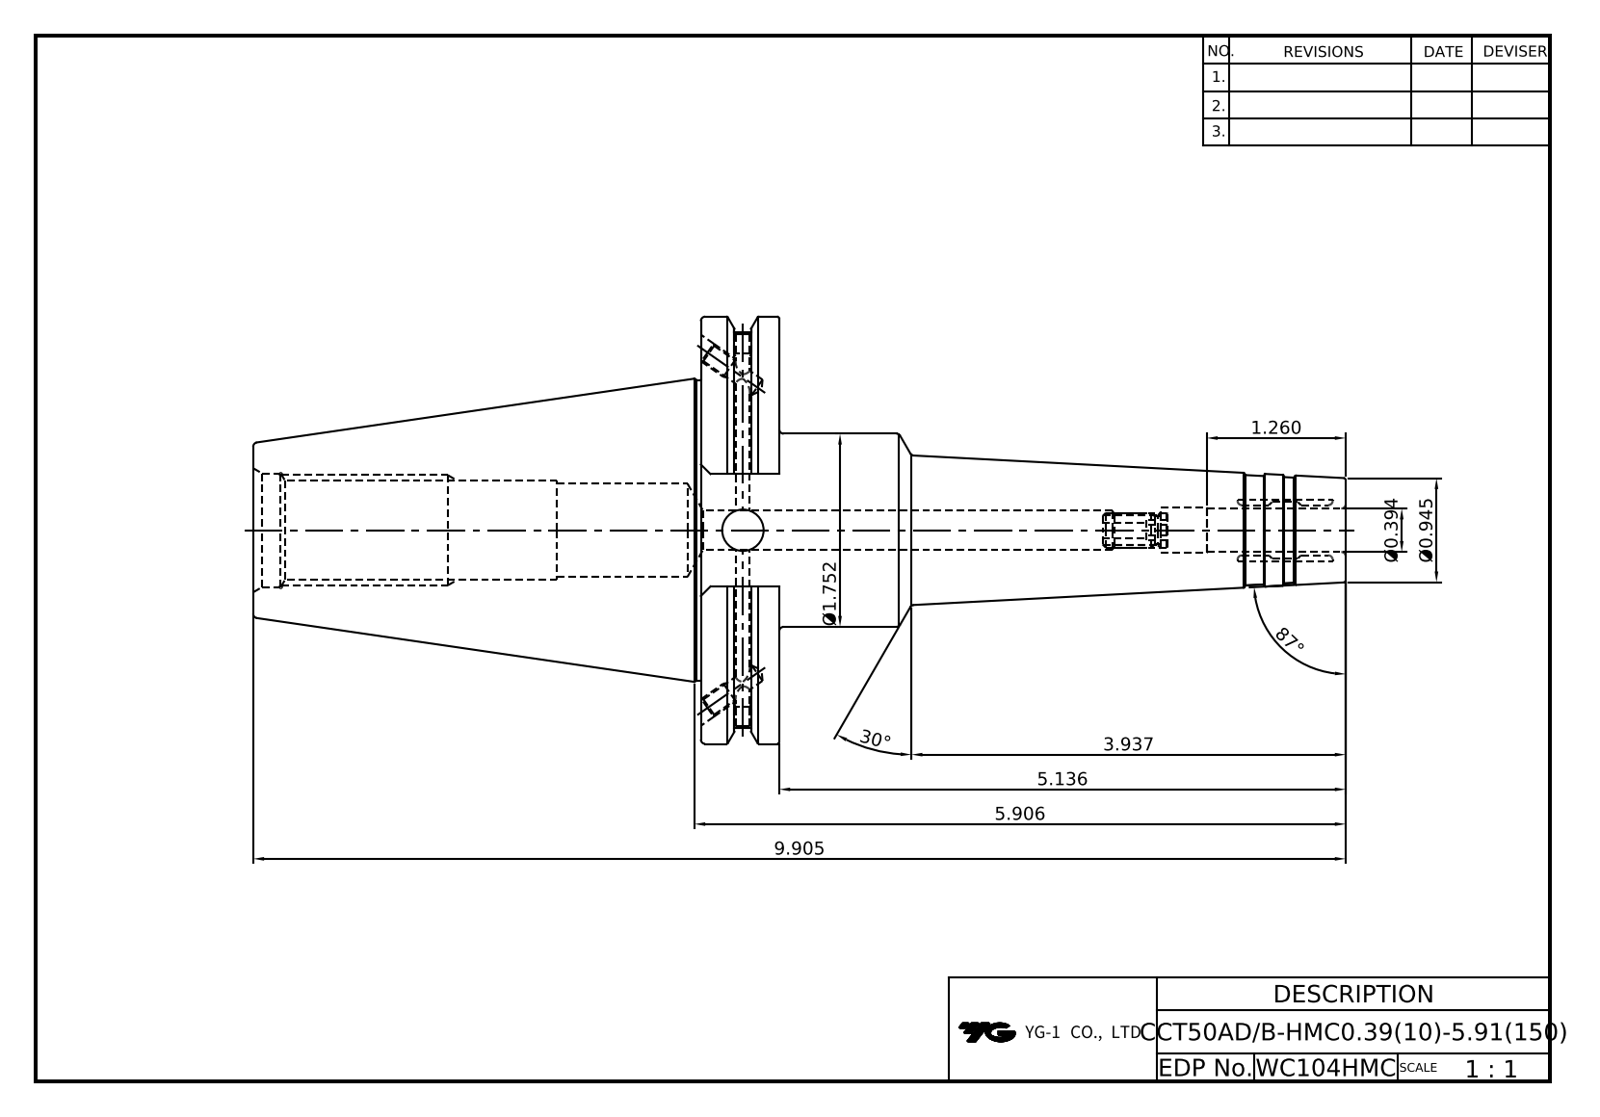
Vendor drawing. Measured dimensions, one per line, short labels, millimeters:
name: LO-CCT50ADB-HMC10-150
written by: Autodesk Inventor 2024 (AUTOMOTIVE_DESIGN)
unit: mm
bodies: 1 solid, 104 faces (38 planar, 26 cylindrical, 40 other)
size: 251.6 × 98.42 × 94.69
volume: 438 009 mm³; area: 60 574 mm²
holes: 2× ⌀3.24, 2× ⌀4.13, 2× ⌀4.2, 2× ⌀5, 1× ⌀6.65, 1× ⌀9.53, 1× ⌀10, 1× ⌀10.6, 1× ⌀21.97, 1× ⌀26.2
bosses: 1× ⌀98.42, 1× ⌀91.29, 1× ⌀69.25, 1× ⌀44.5
face distances: 17.55, 103.1, 120.65, 73.03, 251.6, 148.5, 130.95, 25.9, 103.5, 0.4
